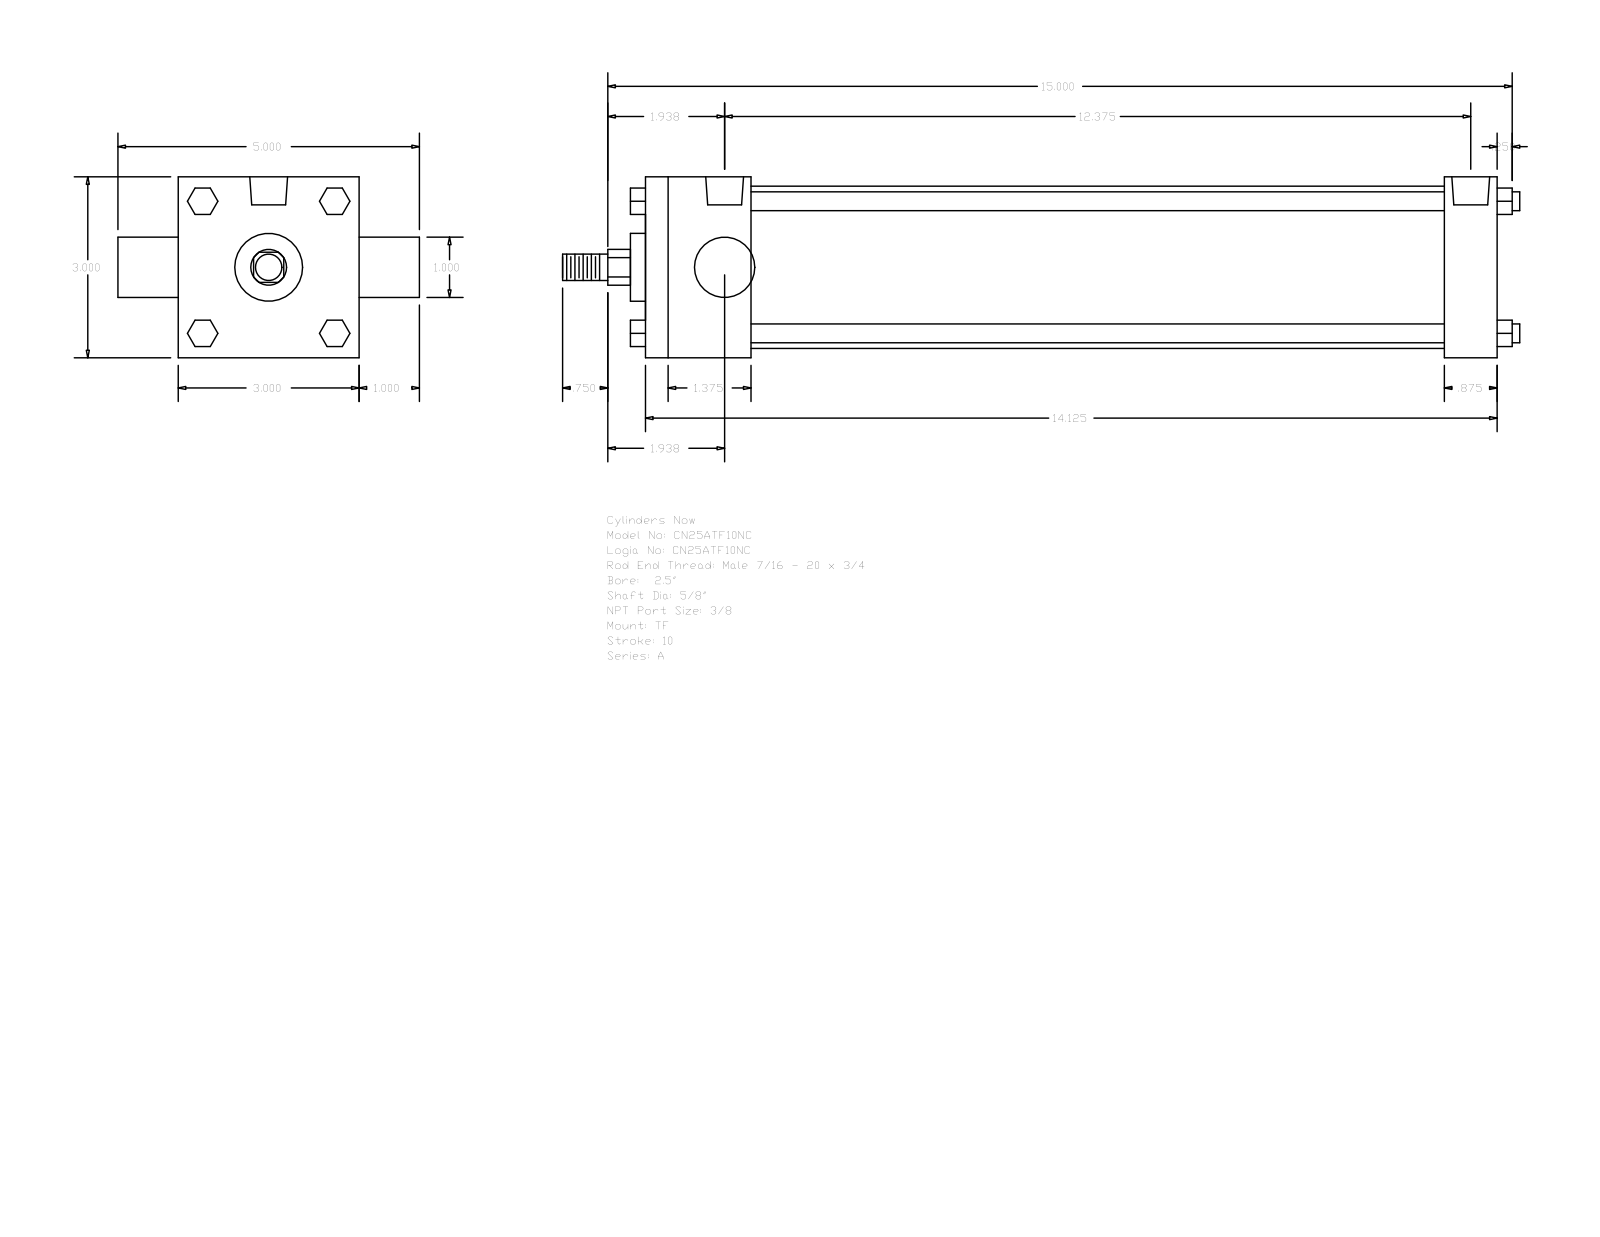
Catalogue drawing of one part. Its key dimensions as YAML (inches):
part_name: "A_TF__0250_0.625"
step_written_by: "GSSL Pune (CONFIG_CONTROL_DESIGN)"
units: inches
bodies: {solids: 0, faces: 120, planar: 92, cylindrical: 28, other: 0}
overall_size: [15.875, 5, 3]
round_holes:
  - {diameter: 0.219, count: 3}
  - {diameter: 0.627, count: 2}
round_bosses_or_shafts:
  - {diameter: 0.313, count: 4}
  - {diameter: 2.69, count: 1}
  - {diameter: 1.125, count: 1}
  - {diameter: 1, count: 1}
  - {diameter: 0.625, count: 1}
  - {diameter: 0.437, count: 1}
partial_cylinders:
  - {radius: 0.297, count: 1}
face_to_face_distances: [3, 14.125, 1.75, 13.25, 11.5, 12.375, 0.875, 1, 4, 0.25]
hole_center_spacings: [0.094, 12.469, 12.375, 12.563]
